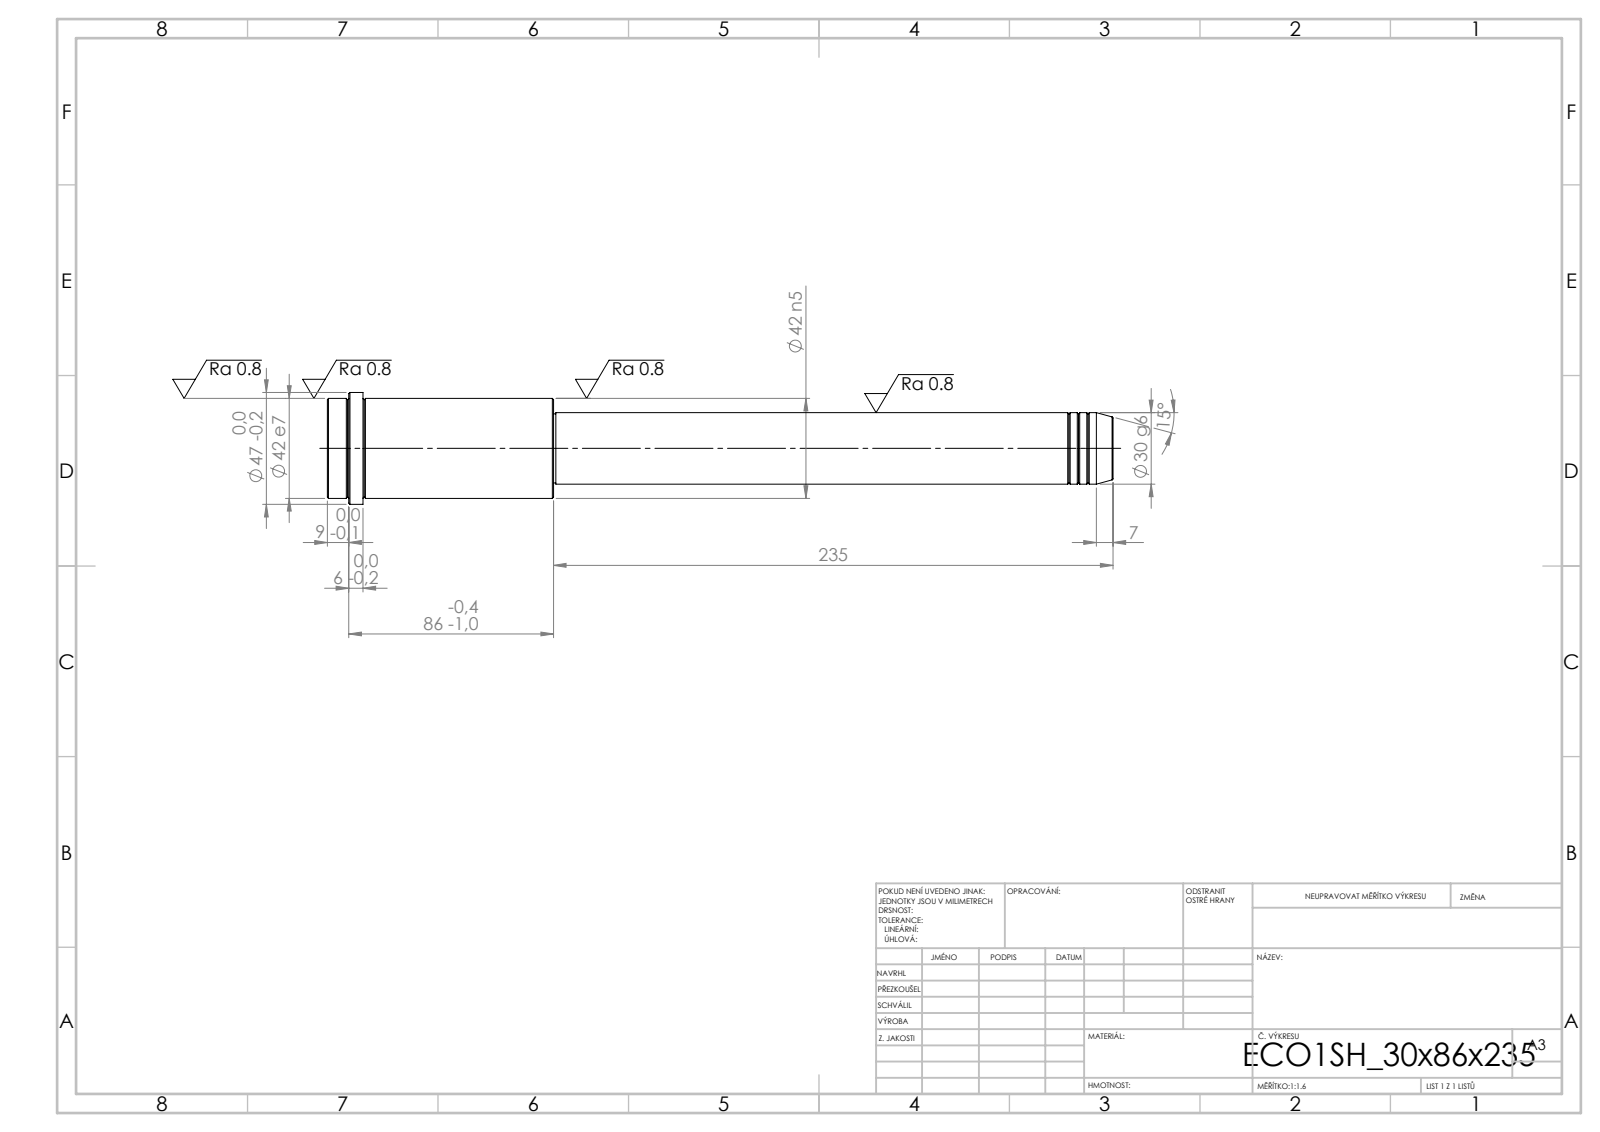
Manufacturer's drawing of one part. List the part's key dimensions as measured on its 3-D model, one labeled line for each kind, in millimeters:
STEP written by: SolidWorks 2019 (CONFIG_CONTROL_DESIGN)
Units: millimetres
Bodies: 1 solid, 52 faces (6 planar, 16 cylindrical, 30 other)
Overall size (bounding box): 330 × 47 × 47
Volume: 298 921 mm³ · Surface area: 38 317 mm²
Round bosses / shafts (diameter × count): ⌀47 ×1, ⌀42 ×1, ⌀30 ×1, ⌀29 ×1
Main face-to-face distances: 95, 235, 330, 315, 80, 15, 321, 86, 6, 9
